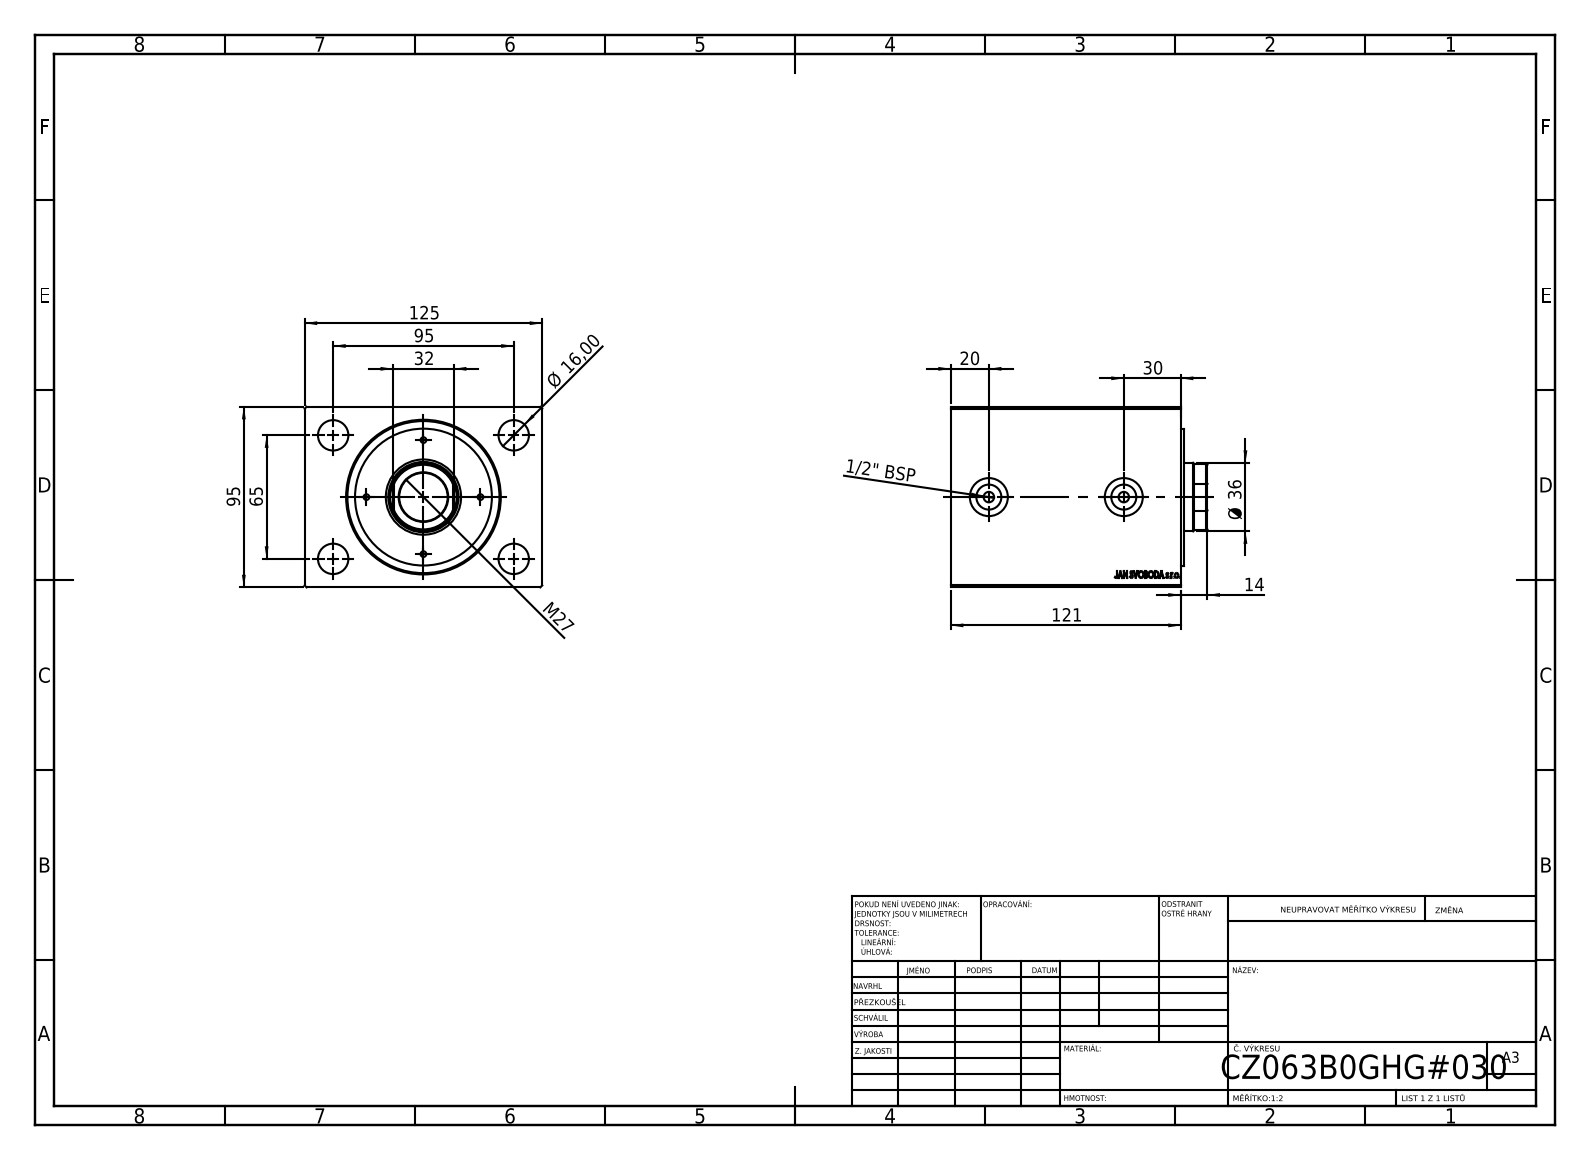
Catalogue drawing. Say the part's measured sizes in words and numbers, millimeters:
The part is named "V500CZ_B_VC; V500CZ". Its 3-D file was written by "SolidWorks 2019 (CONFIG_CONTROL_DESIGN)". It is 3 solids with 874 faces: 400 planar, 58 cylindrical and 416 other. Overall it measures 135 by 125 by 95 millimeters. Its volume is 1 315 000 cubic millimeters and its surface area 149 170 square millimeters. Round holes: 4 of diameter 3, 4 of diameter 16, 2 of diameter 5.5, 2 of diameter 13.16, 2 of diameter 20, 1 of diameter 25.5, 1 of diameter 36, 1 of diameter 37, 1 of diameter 63, 1 of diameter 80. Round bosses or shafts: 1 of diameter 72. Partial cylindrical surfaces (rounded edges, fillets, slot ends): 1 of radius 17.5. The main face-to-face distances are 95, 125, 121, 100.2, 20.8, 14, 1.8, 12.2, 88, 108.8. The hole center spacings are 30, 36.91, 42.43, 47.57, 57.55, 78.5, 84.04, 60.
